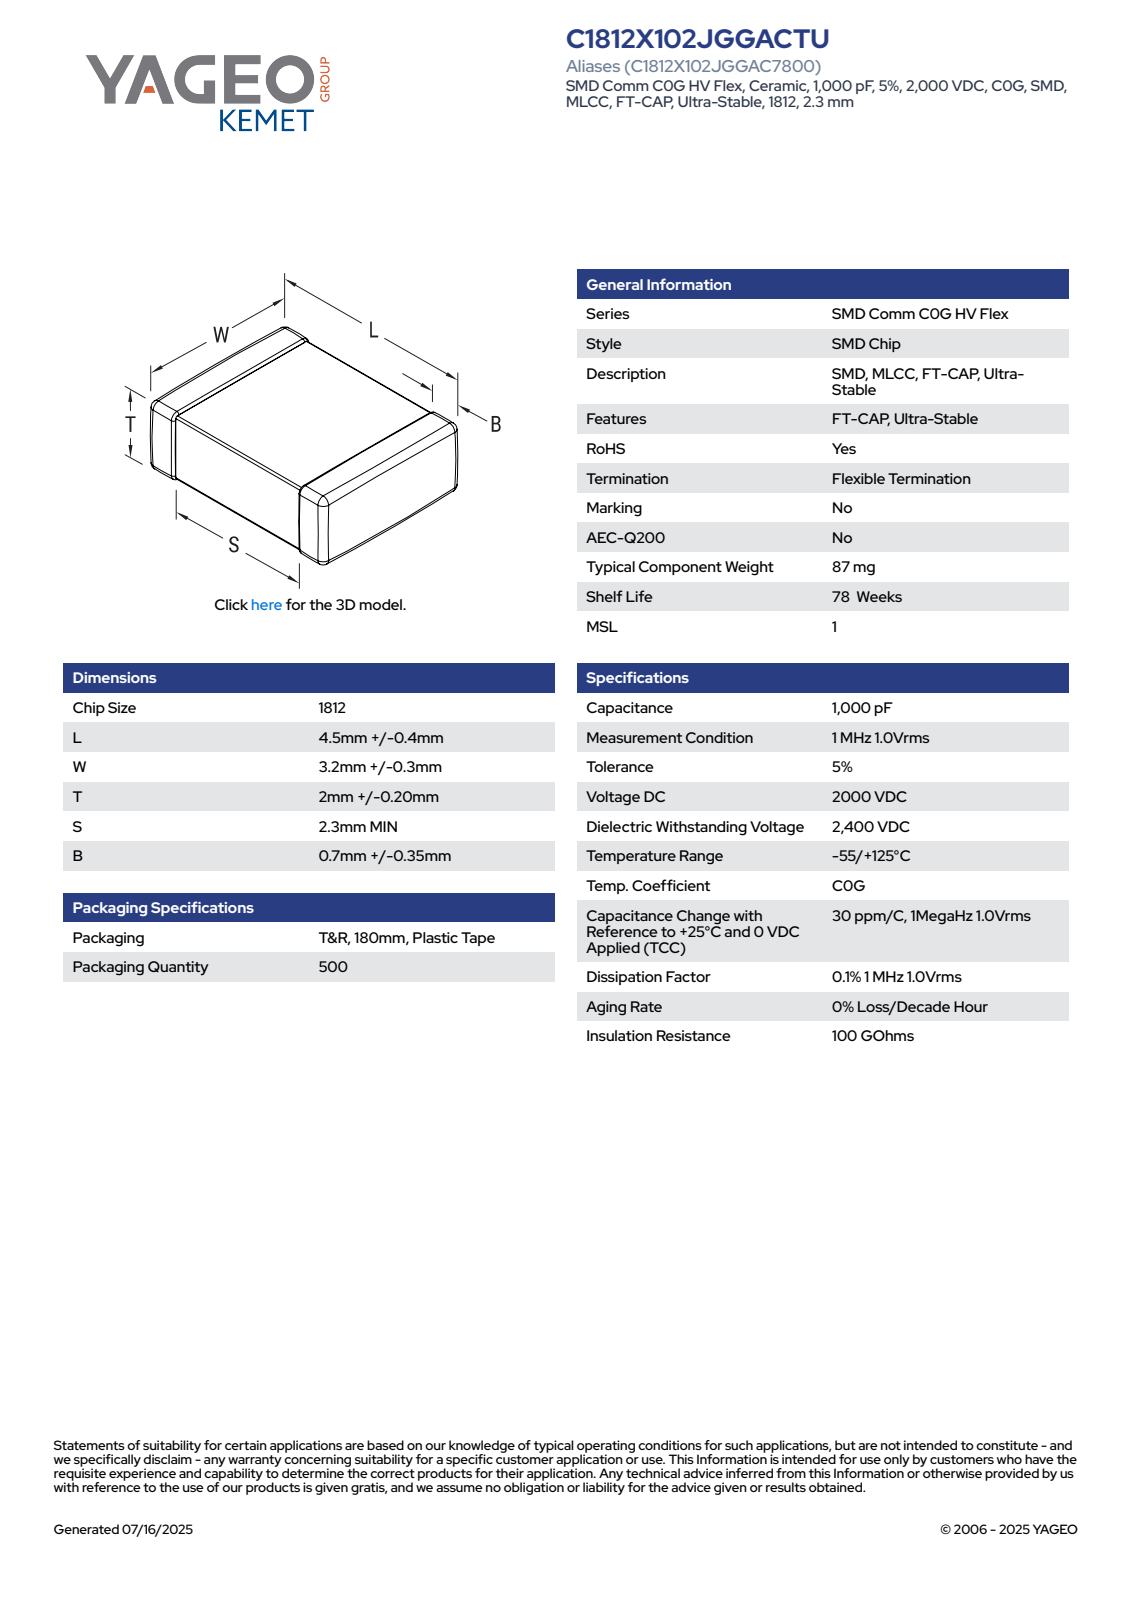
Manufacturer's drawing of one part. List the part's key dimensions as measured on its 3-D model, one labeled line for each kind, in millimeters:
Part name (STEP PRODUCT): CCS_CCSTDNOS_1812_L4.9W3.5T2.2B1.05
STEP written by: SolidWorks 2014 (AUTOMOTIVE_DESIGN)
Units: millimetres
Bodies: 4 solids, 125 faces (71 planar, 38 cylindrical, 16 other)
Overall size (bounding box): 4.9 × 3.5 × 2.2
Volume: 35 mm³ · Surface area: 70 mm²
Main face-to-face distances: 2.13, 2.06, 3.43, 4.9, 2.2, 3.36, 3.5, 1.42, 1.94, 1.49
